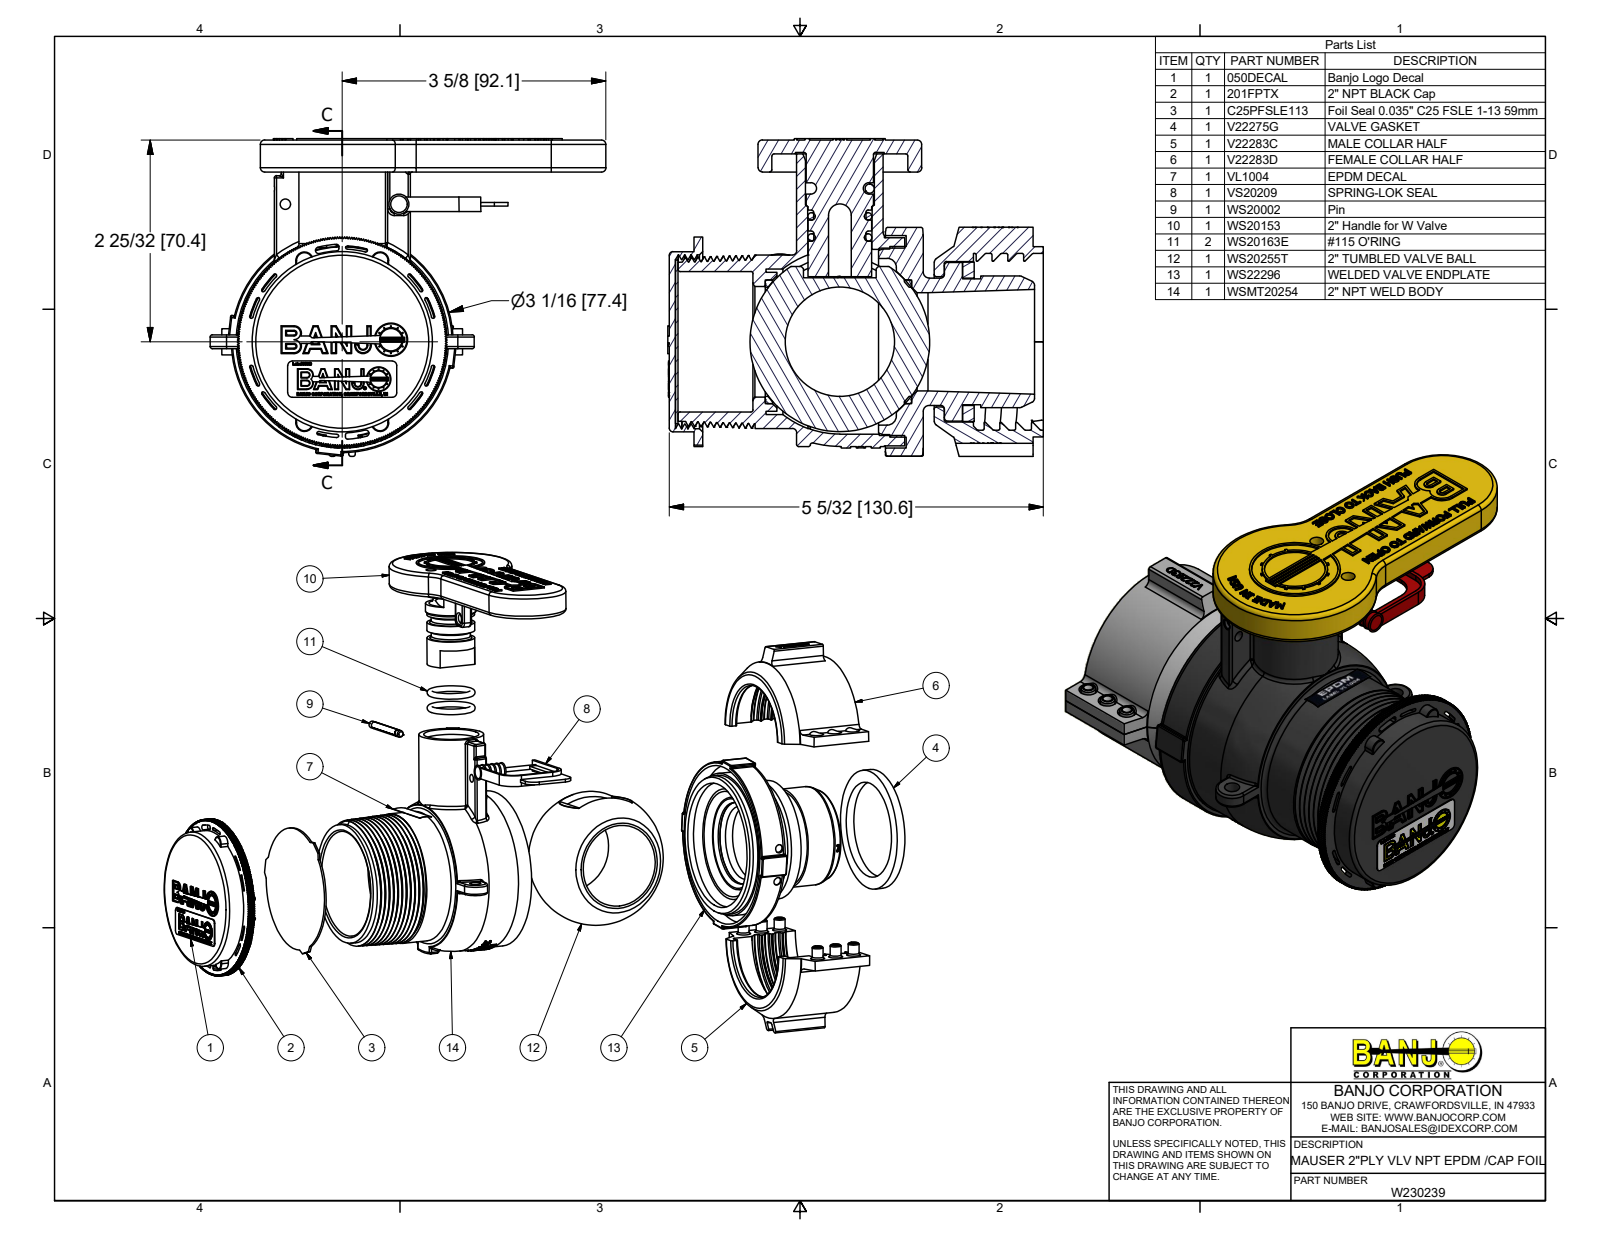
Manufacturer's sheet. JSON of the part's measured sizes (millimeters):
{"part_name": "W230239; WSMT20254; WSMT20254X; V22275G (+8 more)", "step_written_by": "Autodesk Inventor 2018 (AUTOMOTIVE_DESIGN)", "units": "millimeters", "bodies": {"solids": 17, "faces": 4668, "planar": 2455, "cylindrical": 977, "other": 1236}, "overall_size": [1020.5, 138.2, 110.9], "volume_mm3": 318200, "surface_area_mm2": 327700, "round_holes": [[5.3, 6], [6.5, 6], [3.7, 2], [3.8, 2], [4.8, 2], [5.3, 2], [38.1, 2], [4, 1], [5.8, 1], [7.8, 1], [7.9, 1], [8.2, 1]], "round_bosses_or_shafts": [[5.1, 6], [57.2, 2], [77.4, 1], [74.2, 1], [73.2, 1], [72.6, 1], [66.5, 1], [66.4, 1]], "partial_cylinders_radius": [[0.8, 76], [0.4, 24], [2.3, 10], [1.5, 4], [1.6, 4], [3, 4], [6.4, 4], [0.3, 3]], "face_to_face_distances": [3, 2.2, 4.8, 0.9, 0.9, 2.2, 85.6, 86.5, 86.5, 88.7], "hole_center_spacings": [73.2, 72.6, 9.5, 9.5, 19.1, 41.5, 51.9, 56.2]}
